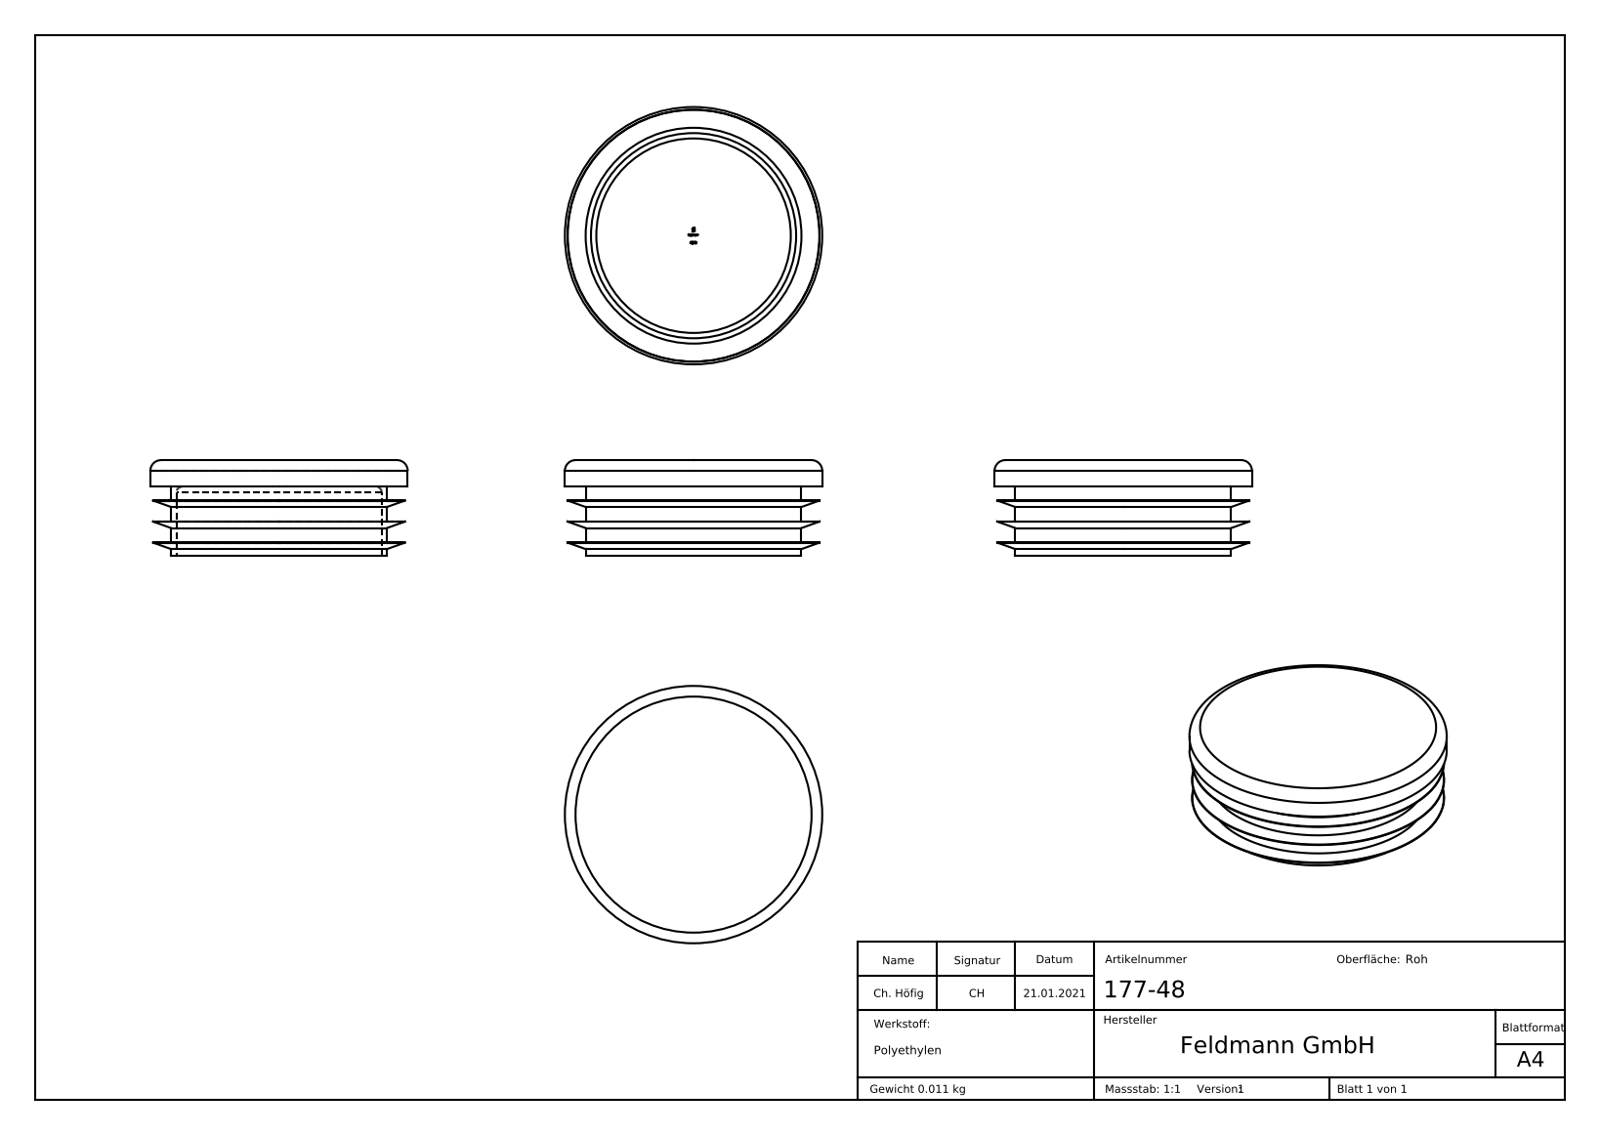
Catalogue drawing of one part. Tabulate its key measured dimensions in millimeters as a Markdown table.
| quantity | value |
| --- | --- |
| part name | 177-48 |
| STEP written by | SolidWorks 2015 (CONFIG_CONTROL_DESIGN) |
| units | millimeters |
| bodies | 1 solid, 201 faces (116 planar, 12 cylindrical, 73 other) |
| overall size | 48.3 × 48.3 × 16.5 |
| volume | 10 740 mm³ |
| surface area | 9 130 mm² |
| round holes (diameter × count) | 39.3 × 1 |
| round bosses / shafts (diameter × count) | 48.3 × 1, 41.3 × 1 |
| main face-to-face distances | 5, 3, 6, 9, 14, 11, 8, 2.5, 5.5, 8.5 |
